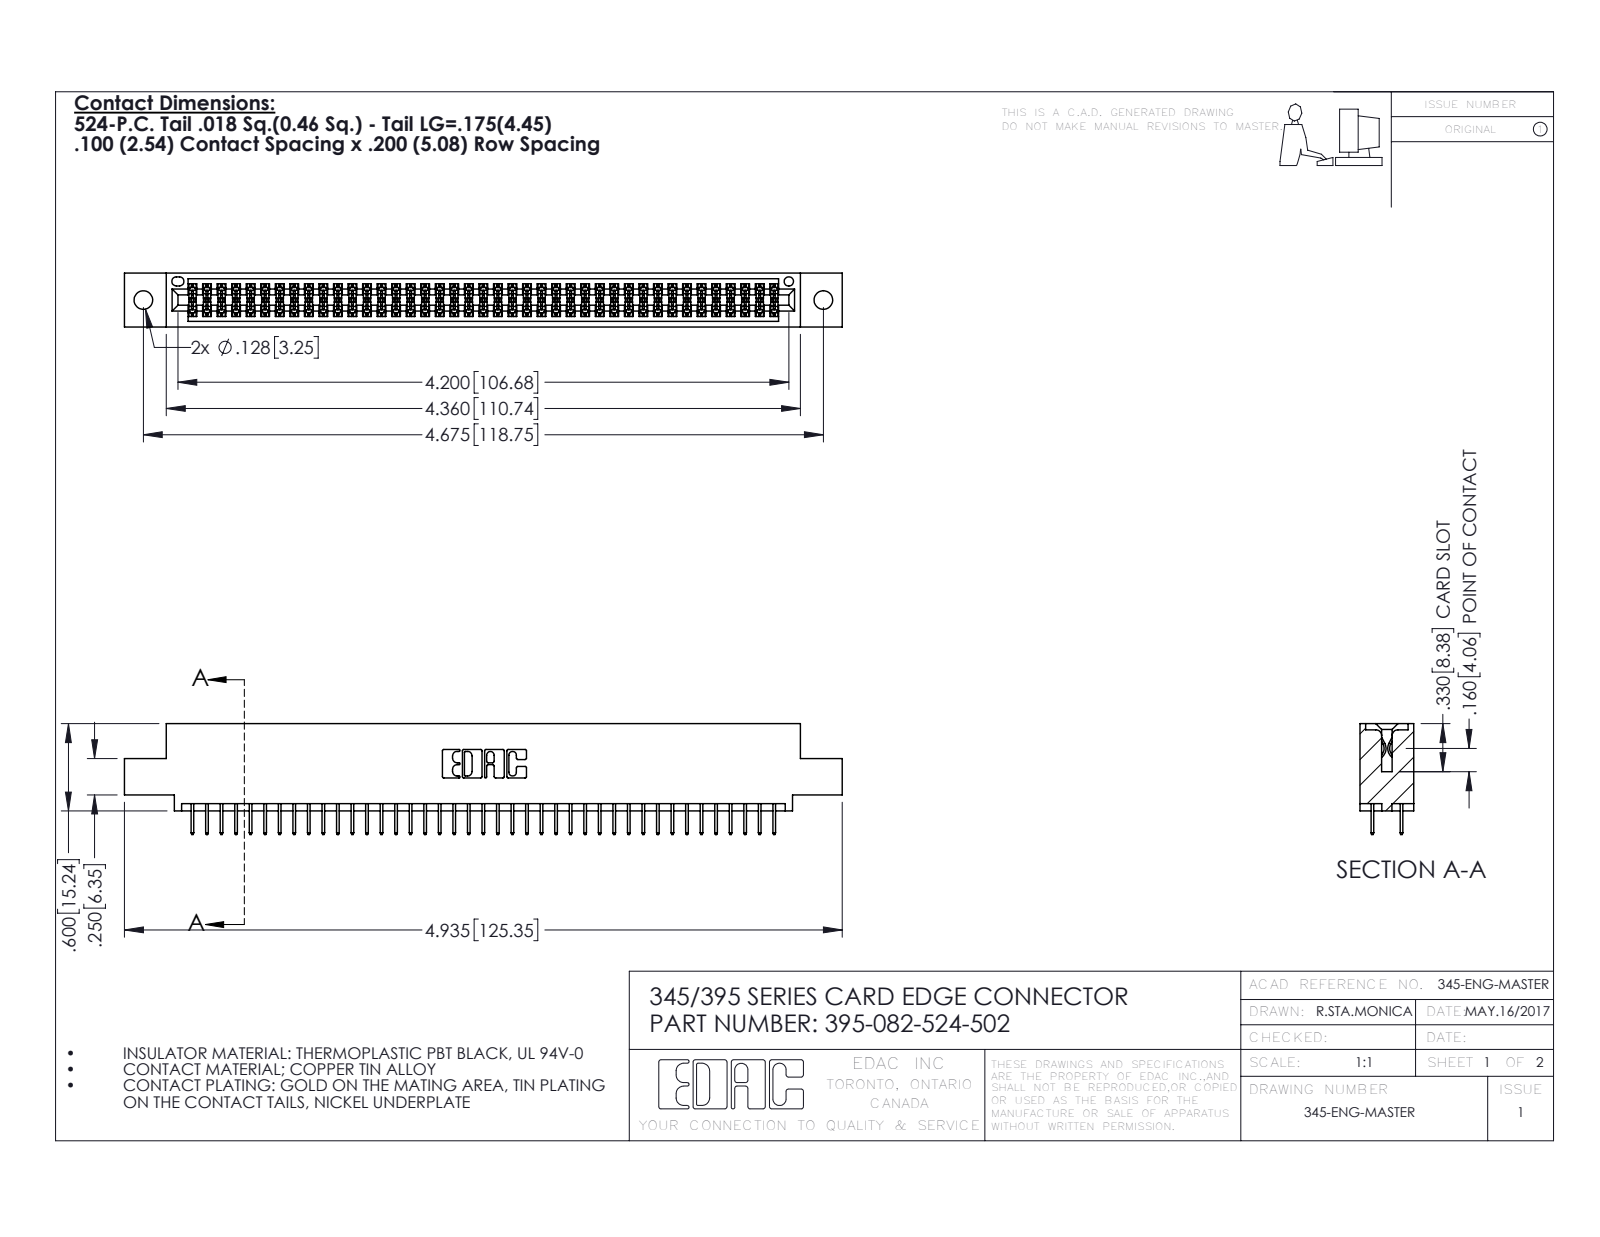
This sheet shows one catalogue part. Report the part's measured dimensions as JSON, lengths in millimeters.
{"part_name": "345 Part_0.110 Offset - 0.128 Dia; 345-292-001_345-293-124; 395-082-524-502", "step_written_by": "SolidWorks 2016 (CONFIG_CONTROL_DESIGN)", "units": "millimeters", "bodies": {"solids": 83, "faces": 4558, "planar": 3282, "cylindrical": 1276, "other": 0}, "overall_size": [125.3, 19.4, 9.4], "volume_mm3": 11900, "surface_area_mm2": 17110, "round_holes": [[3.3, 2], [1.6, 1]], "partial_cylinders_radius": [[0.2, 123], [0.3, 22], [0.2, 6], [0.8, 6], [0.7, 3], [0.4, 2], [0.5, 2], [0.6, 2]], "face_to_face_distances": [1.8, 7.6, 9.4, 5.1, 2.5, 6.9, 0.6, 5.7, 1.8, 4.4], "hole_center_spacings": [6.9, 112.8, 118.7]}
